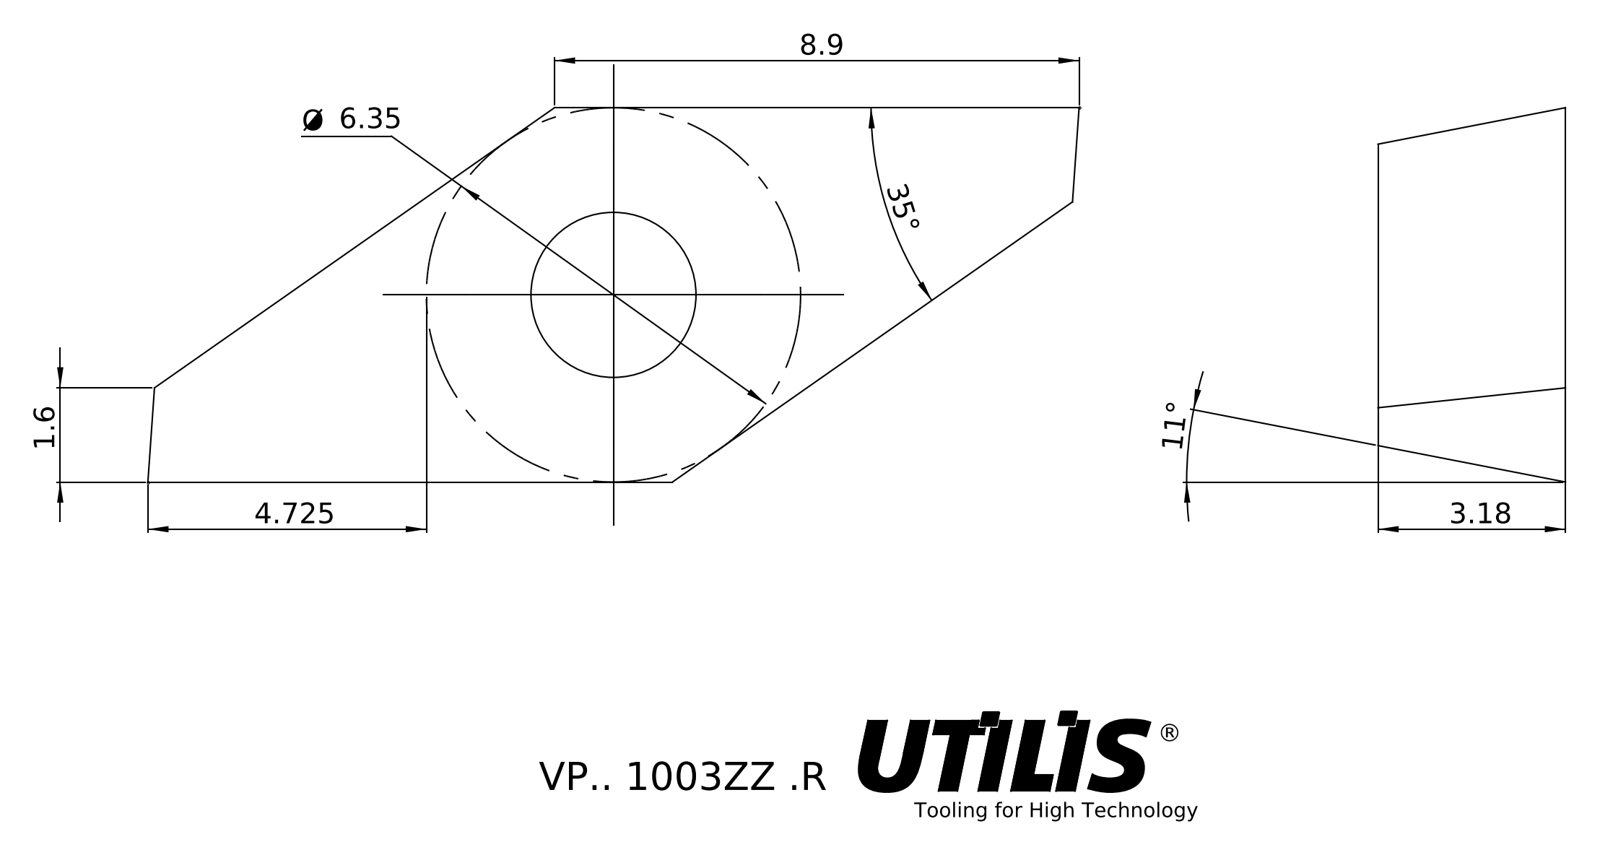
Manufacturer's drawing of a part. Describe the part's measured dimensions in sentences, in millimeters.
The part is named "VP.. 1003ZZ .R". Its 3-D file was written by "SolidWorks 2016 (AUTOMOTIVE_DESIGN)". It is 1 solid with 10 faces: 8 planar, 2 cylindrical and 0 other. Overall it measures 15.8 by 6.35 by 3.18 millimeters. Its volume is 158 cubic millimeters and its surface area 242 square millimeters. Round holes: 1 of diameter 2.8. The main face-to-face distances are 3.18.
